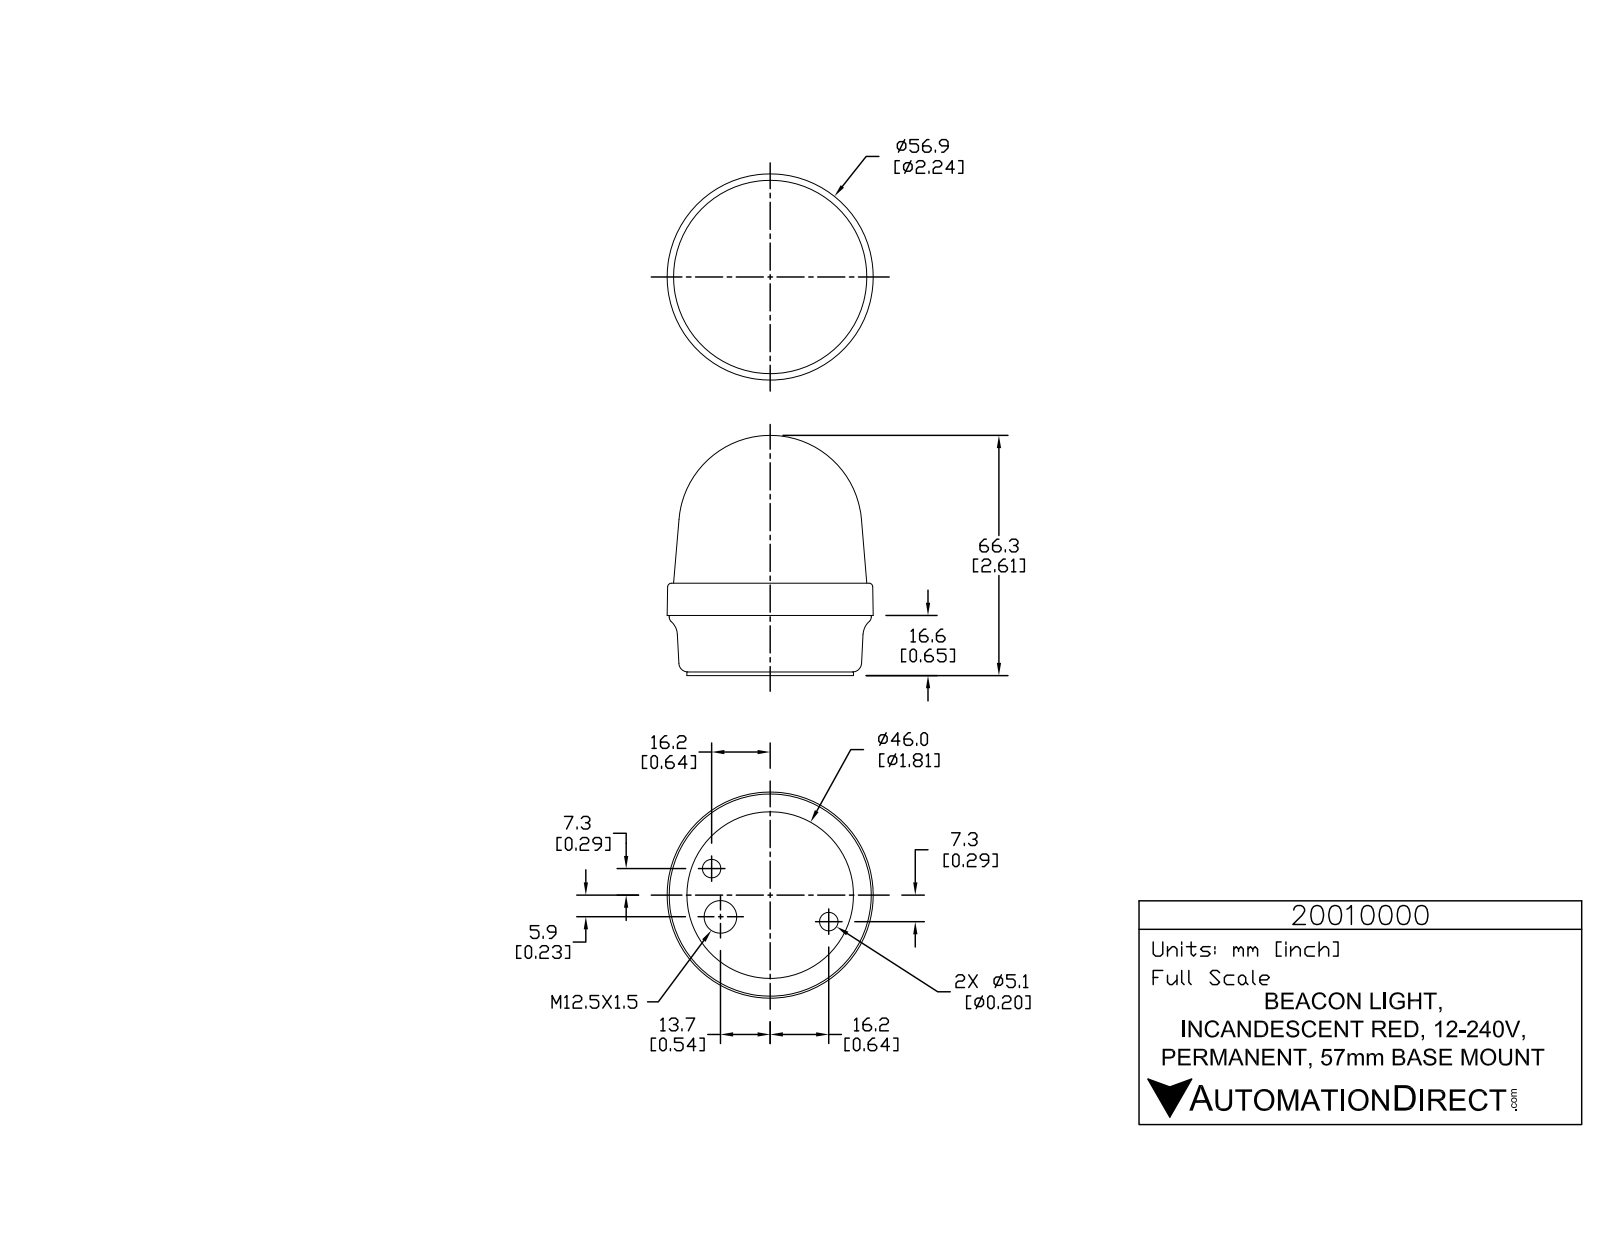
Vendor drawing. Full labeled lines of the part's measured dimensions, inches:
Part name (STEP PRODUCT): 20010000
STEP written by: SolidWorks 2015 (AUTOMOTIVE_DESIGN)
Units: inches
Bodies: 1 solid, 781 faces (526 planar, 163 cylindrical, 92 other)
Overall size (bounding box): 2.61 × 2.24 × 2.24
Volume: 7.533 in³ · Surface area: 20.69 in²
Round holes (diameter × count): ⌀0.039 ×3, ⌀0.201 ×2, ⌀0.354 ×1
Round bosses / shafts (diameter × count): ⌀0.226 ×3, ⌀0.056 ×3, ⌀2.197 ×1, ⌀1.811 ×1
Partial cylindrical surfaces — rounded edges, fillets, slot ends (radius × count): R0.008 ×6, R0.008 ×6, R0.008 ×6, R0.131 ×6, R0.004 ×3, R0.005 ×3, R0.008 ×3, R0.008 ×3
Main face-to-face distances: 0.039, 0.654, 0.614, 1.004, 0.965, 0.35, 0.697, 1.351, 1.311, 0.347
Hole centre spacings: 0.534, 1.179, 1.398
